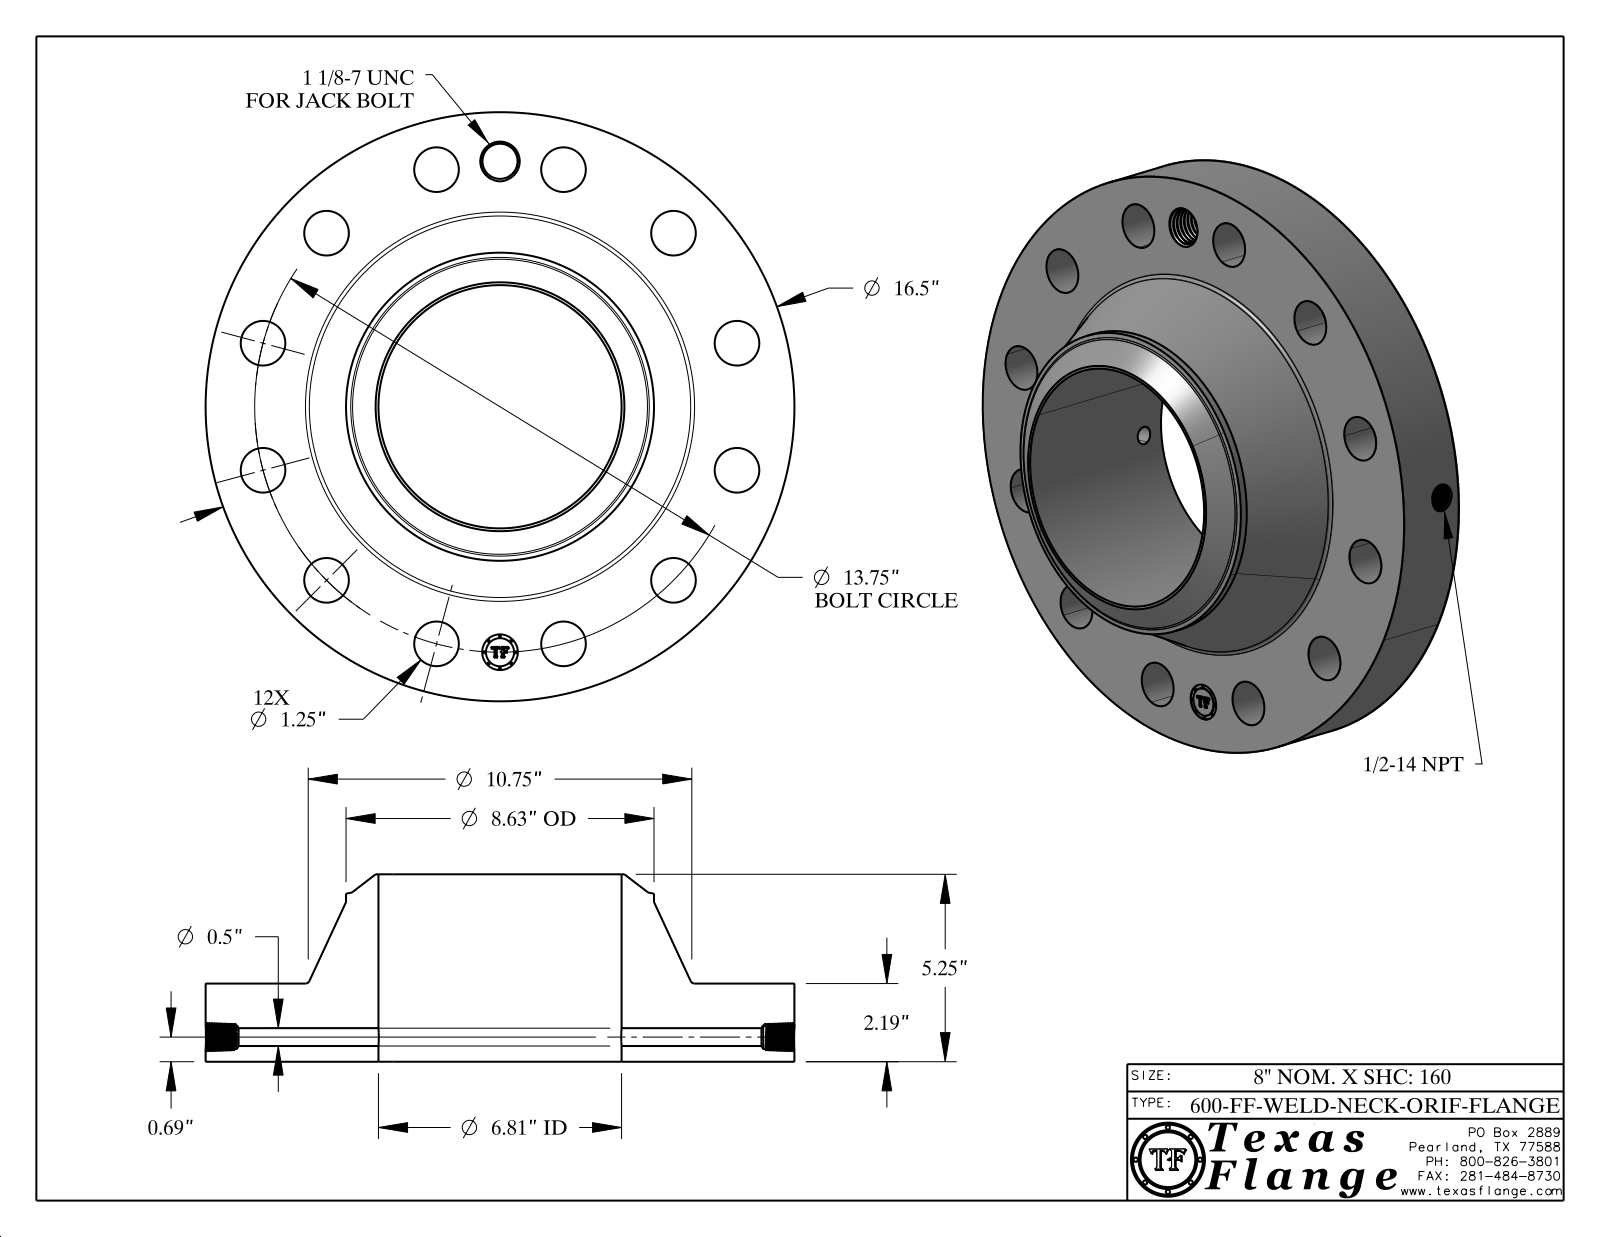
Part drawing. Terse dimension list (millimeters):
name: 600-FF-WELD-NECK
written by: CATIA V5 STEP AP214 (AUTOMOTIVE_DESIGN)
unit: mm
bodies: 1 solid, 781 faces (368 planar, 100 cylindrical, 313 other)
size: 419.1 × 419.1 × 133.4
volume: 7 348 000 mm³; area: 474 800 mm²
holes: 12× ⌀31.8, 1× ⌀12.7, 1× ⌀17.1, 1× ⌀25, 1× ⌀25.4, 1× ⌀173.1
bosses: 8× ⌀1.5, 1× ⌀419.1, 1× ⌀219.2, 1× ⌀20
face distances: 55.6, 133.4, 77.7, 0.4, 55.2, 78.1, 7.6, 7.4, 1.4, 6.3
hole spacings: 174.6, 302.5, 90.4, 174.6, 246.9, 337.3, 45.6, 90.4
